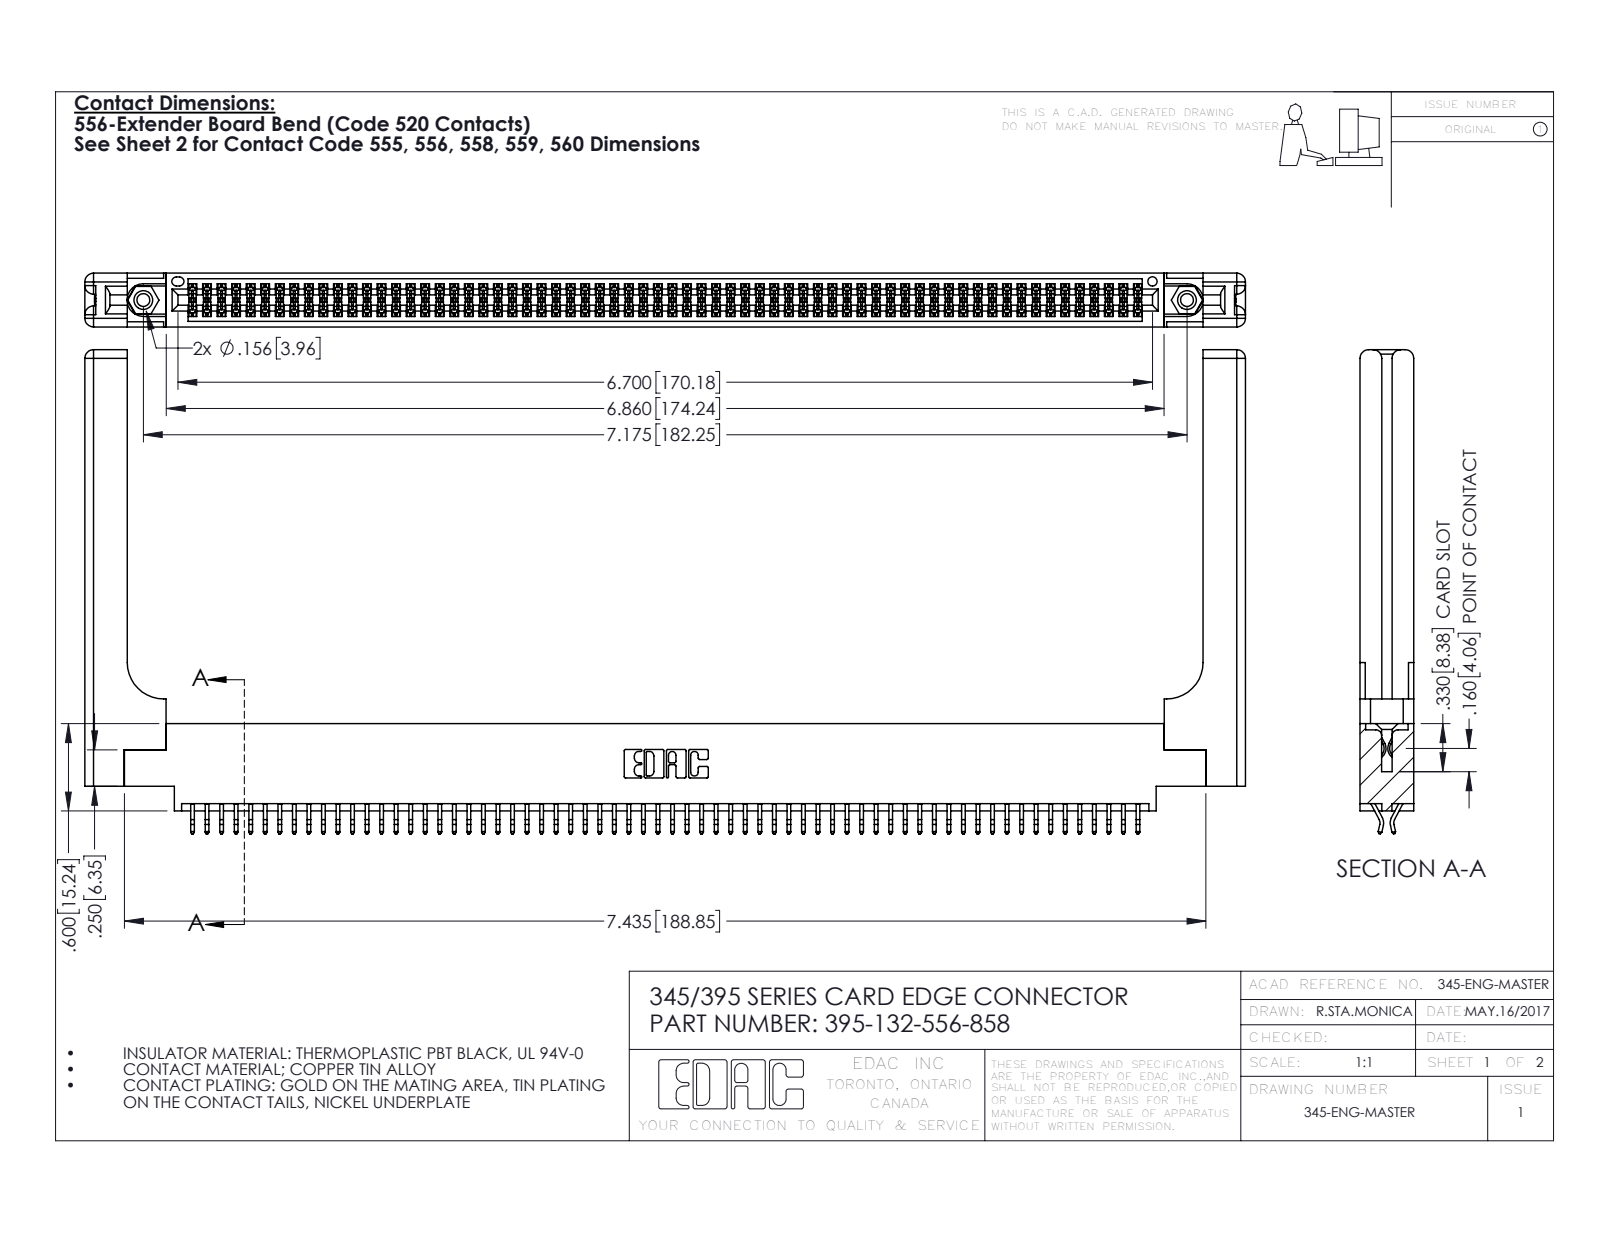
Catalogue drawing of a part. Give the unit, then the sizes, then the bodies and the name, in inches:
Units: inches
Overall size (bounding box): 7.979 × 3.327 × 0.37
Round holes (diameter × count): ⌀0.089 ×2, ⌀0.125 ×2, ⌀0.156 ×2, ⌀0.064 ×1
Round bosses / shafts (diameter × count): ⌀0.155 ×2
Partial cylindrical surfaces — rounded edges, fillets, slot ends (radius × count): R0.006 ×198, R0.01 ×22, R0.06 ×16, R0.007 ×6, R0.031 ×6, R0.026 ×3, R0.01 ×2, R0.014 ×2
Main face-to-face distances: 0.072, 0.298, 0.37, 0.025, 0.098, 0.272, 0.2, 0.225, 0.175, 0.148
Hole centre spacings: 0.27, 6.939, 7.175
Volume: 1.725 in³ · Surface area: 53.95 in²
Bodies: 137 solids, 7778 faces (5116 planar, 2602 cylindrical, 60 other)
Part name (STEP PRODUCT): 345-292-001_556 Tail; 345-220-058_345-220-058; 395-132-556-858; 345-250-001_345-250-001-102 (+1 more)
STEP written by: SolidWorks 2016 (CONFIG_CONTROL_DESIGN)
